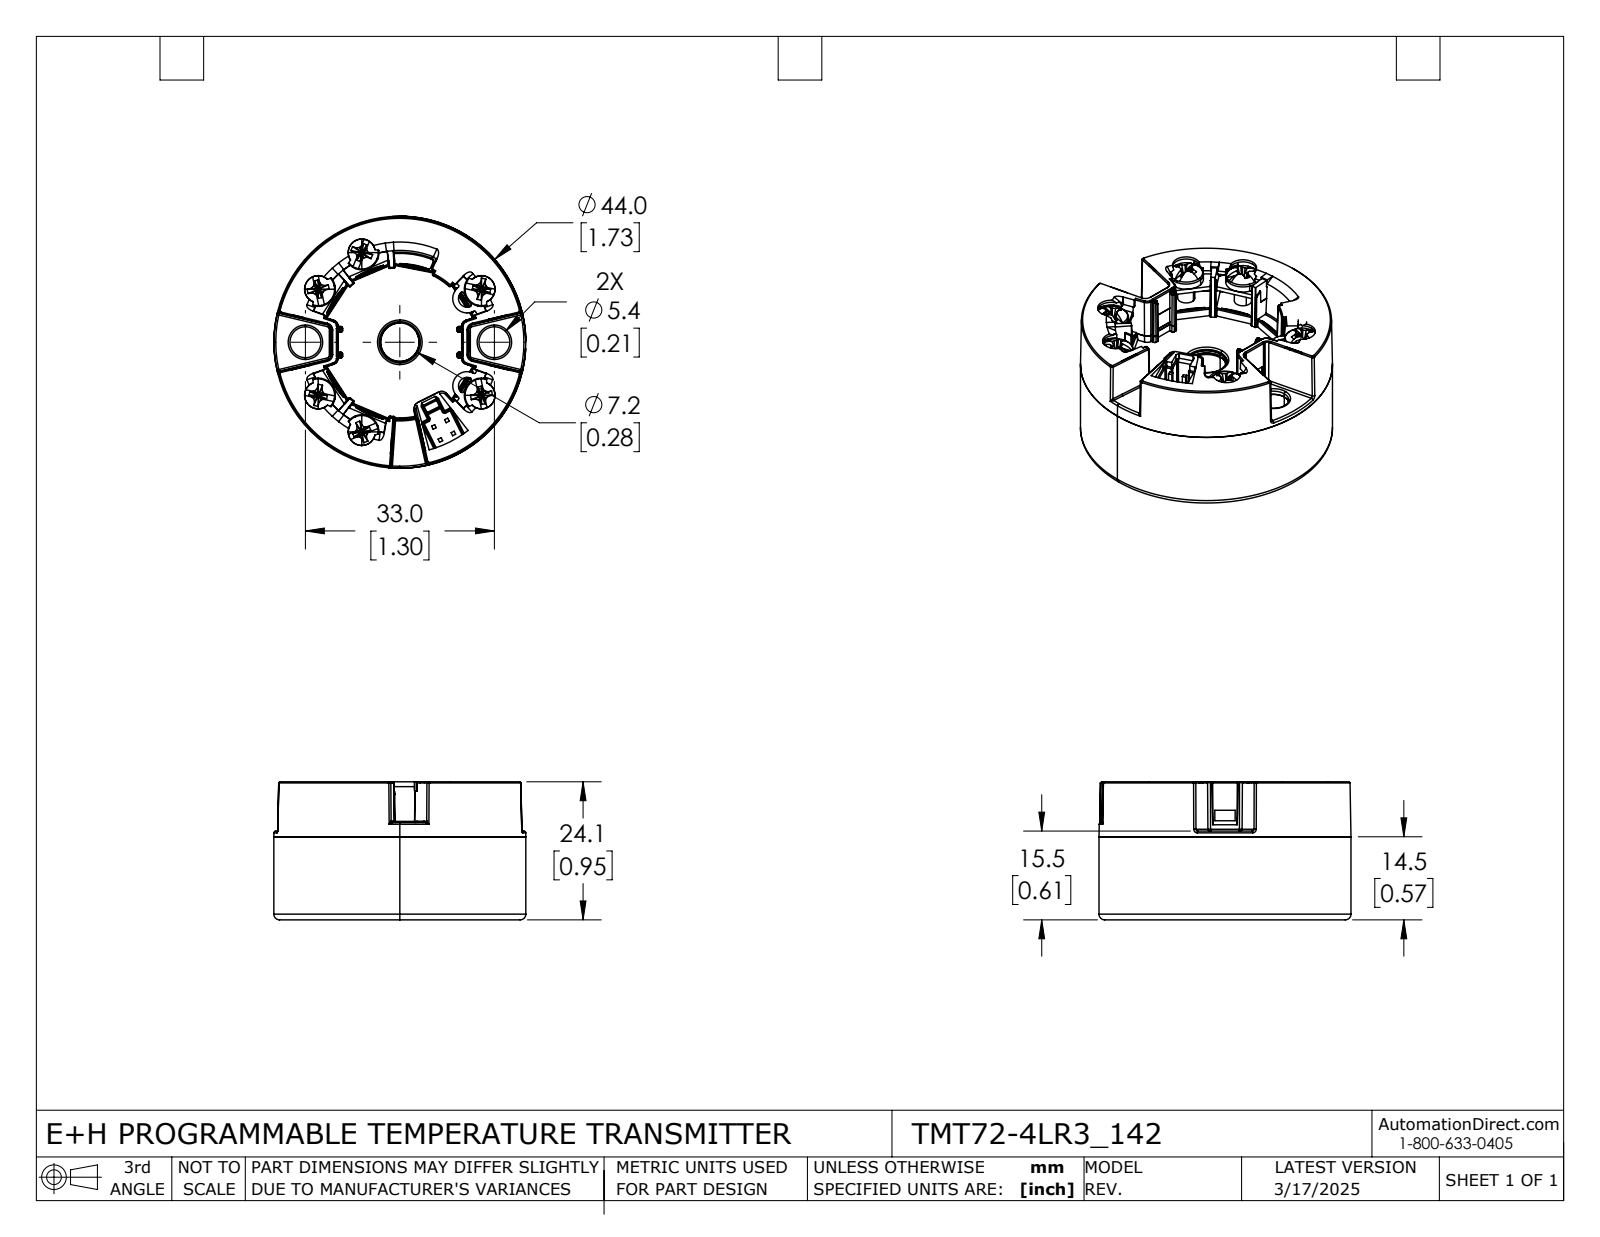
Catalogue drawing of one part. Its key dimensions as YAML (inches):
part_name: "TMT72-4LR3_142"
step_written_by: "SolidWorks 2024 (AUTOMOTIVE_DESIGN)"
units: inches
bodies: {solids: 14, faces: 1114, planar: 432, cylindrical: 282, other: 400}
overall_size: [1.732, 1.732, 1.008]
volume: 1.727
surface_area: 15.77
round_holes:
  - {diameter: 0.055, count: 5}
  - {diameter: 0.118, count: 4}
  - {diameter: 0.126, count: 2}
  - {diameter: 0.176, count: 2}
  - {diameter: 0.213, count: 1}
  - {diameter: 0.265, count: 1}
  - {diameter: 0.283, count: 1}
round_bosses_or_shafts:
  - {diameter: 0.236, count: 6}
  - {diameter: 0.126, count: 4}
  - {diameter: 0.039, count: 4}
  - {diameter: 0.055, count: 3}
  - {diameter: 0.118, count: 2}
  - {diameter: 0.339, count: 1}
  - {diameter: 0.094, count: 1}
partial_cylinders:
  - {radius: 0.008, count: 76}
  - {radius: 0.012, count: 14}
  - {radius: 0.028, count: 12}
  - {radius: 0.039, count: 12}
  - {radius: 0.02, count: 10}
  - {radius: 0.059, count: 3}
  - {radius: 0.073, count: 2}
  - {radius: 0.098, count: 2}
face_to_face_distances: [0.61, 0.339, 0.949, 0.059, 0.217, 0.827, 0.122, 0.031, 0.063, 0.28]
hole_center_spacings: [0.669, 0.229, 0.375, 0.797, 1.265, 0.27, 0.643, 1.324]
